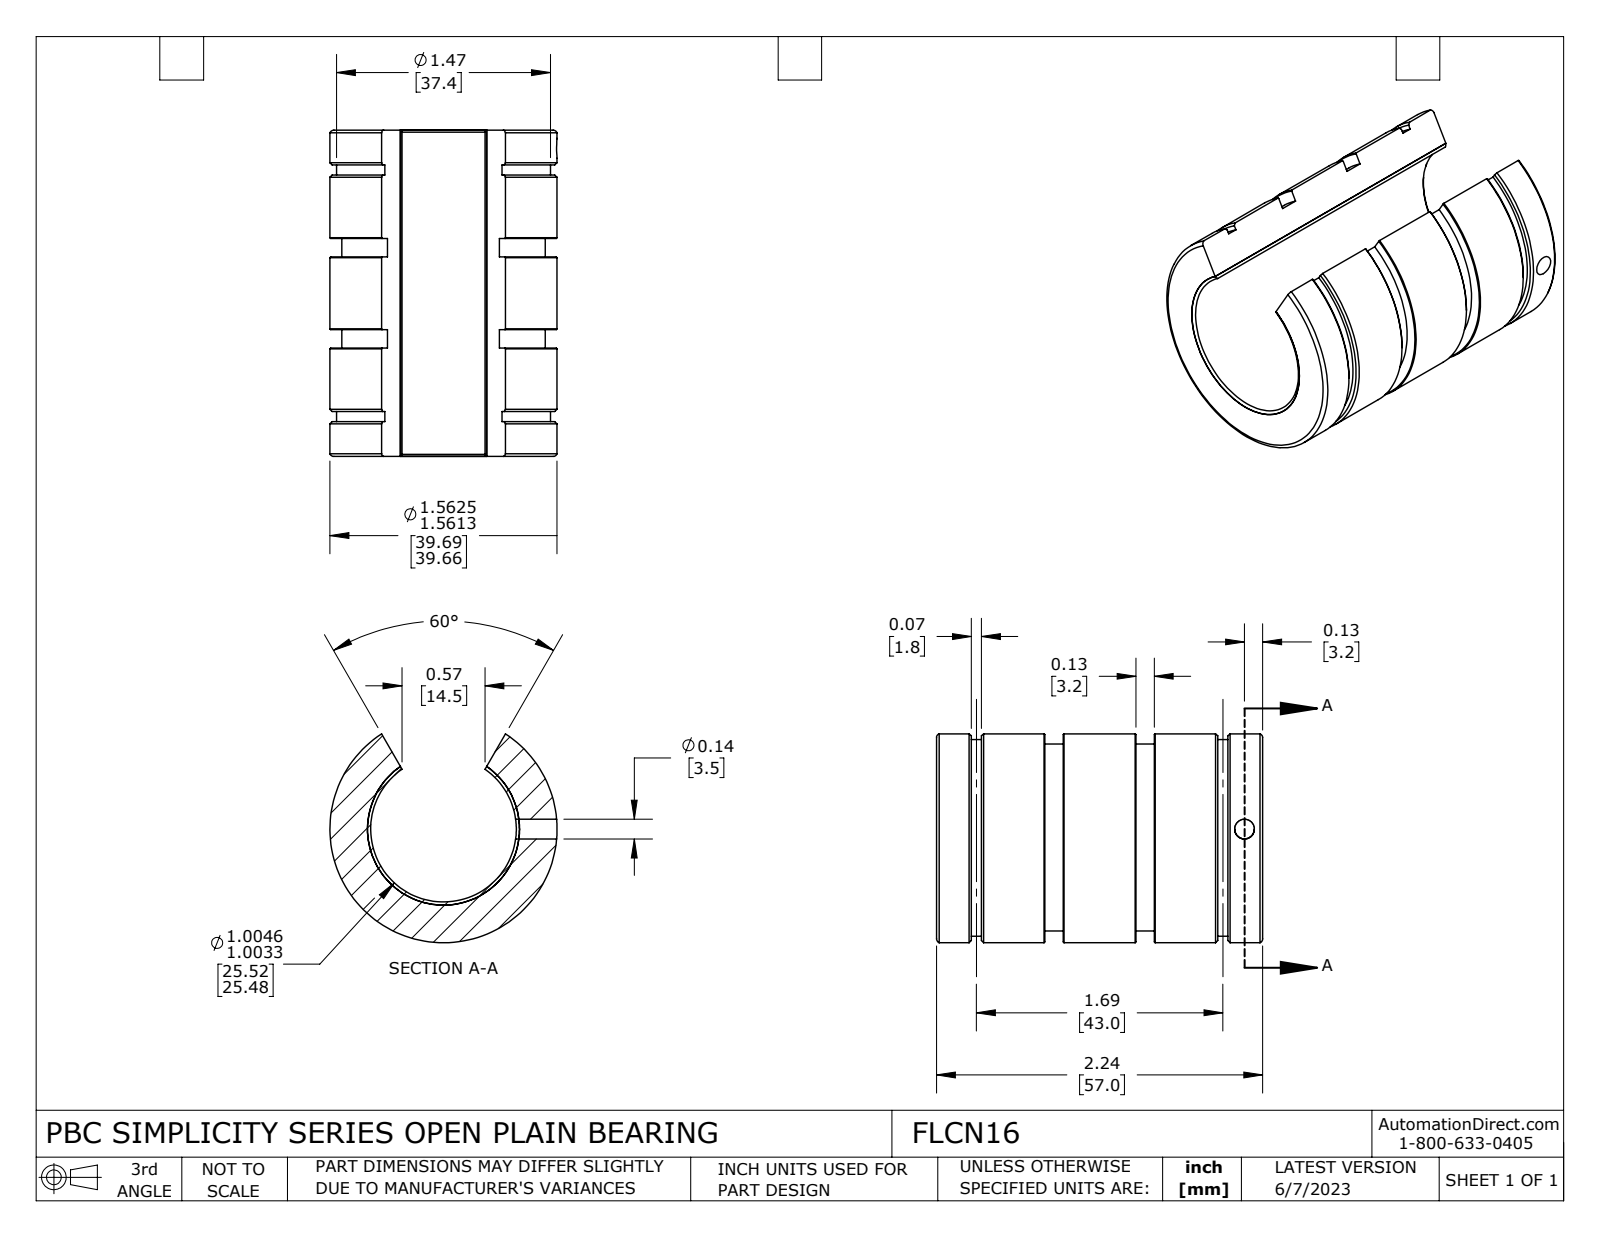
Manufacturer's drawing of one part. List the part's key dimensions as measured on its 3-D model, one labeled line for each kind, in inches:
Part name (STEP PRODUCT): FLCN16
STEP written by: SolidWorks 2021 (CONFIG_CONTROL_DESIGN)
Units: inches
Bodies: 2 solids, 82 faces (14 planar, 40 cylindrical, 28 other)
Overall size (bounding box): 2.243 × 1.562 × 1.435
Volume: 1.946 in³ · Surface area: 31.13 in²
Round holes (diameter × count): ⌀0.136 ×1, ⌀1.001 ×1, ⌀1.045 ×1
Round bosses / shafts (diameter × count): ⌀1.562 ×1, ⌀1.471 ×1, ⌀1.399 ×1
Main face-to-face distances: 2.243, 0.745, 1.497, 0.871, 1.371, 0.126, 0.626, 0.752, 0.5, 0.239
